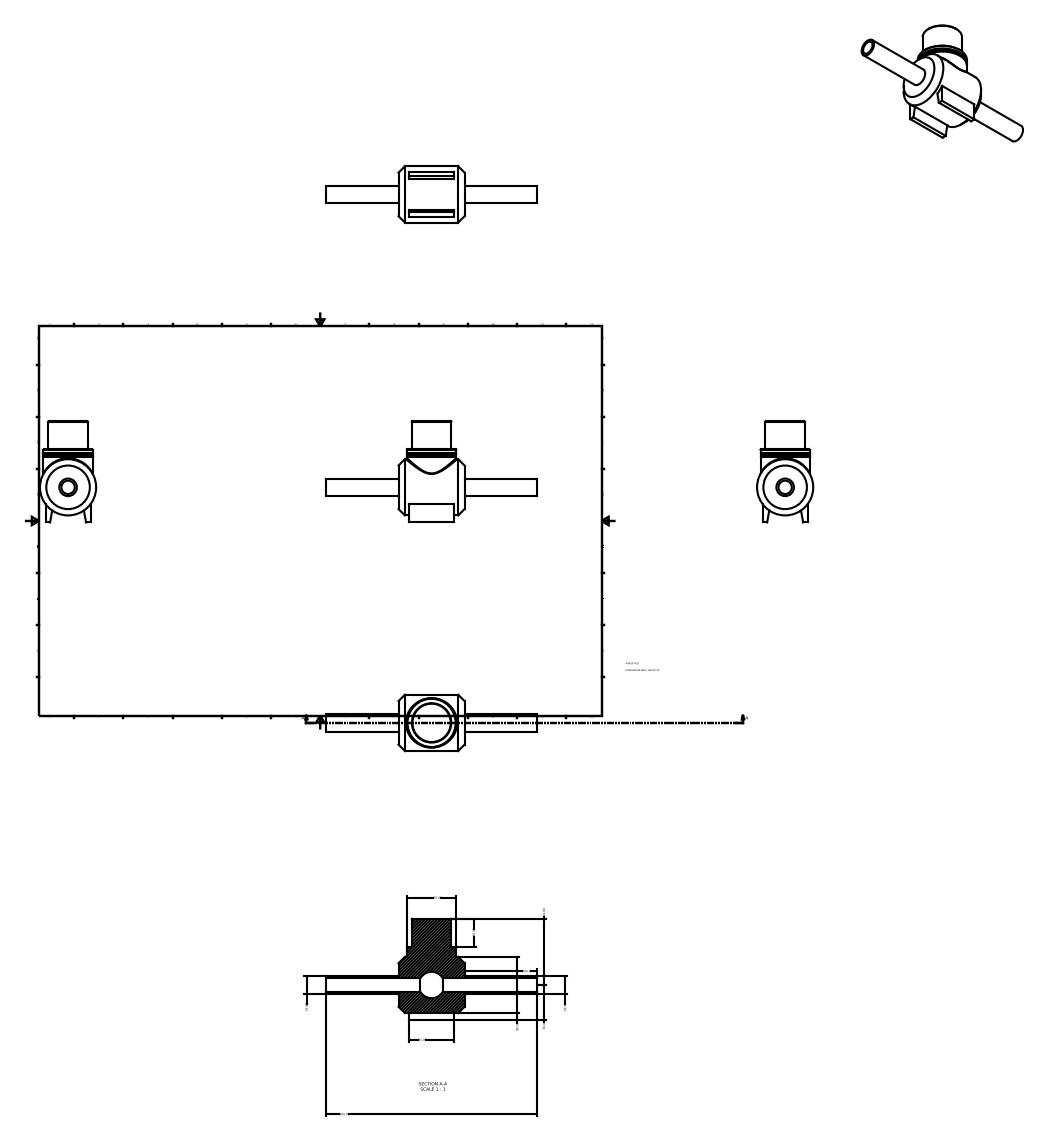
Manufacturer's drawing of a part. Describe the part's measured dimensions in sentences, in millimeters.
The part is named "436207025". Its 3-D file was written by "Autodesk Inventor 2015 (AUTOMOTIVE_DESIGN)". It is 1 solid with 33 faces: 16 planar, 9 cylindrical and 8 other. Overall it measures 300 by 144 by 80 millimeters. Its volume is 643 059 cubic millimeters and its surface area 83 404 square millimeters. Round holes: 1 of diameter 19. Round bosses or shafts: 1 of diameter 80, 1 of diameter 70, 1 of diameter 56, 1 of diameter 25. The main face-to-face distances are 94, 64, 40, 104, 144, 14.5, 79.5, 103, 117.5, 182.5.
